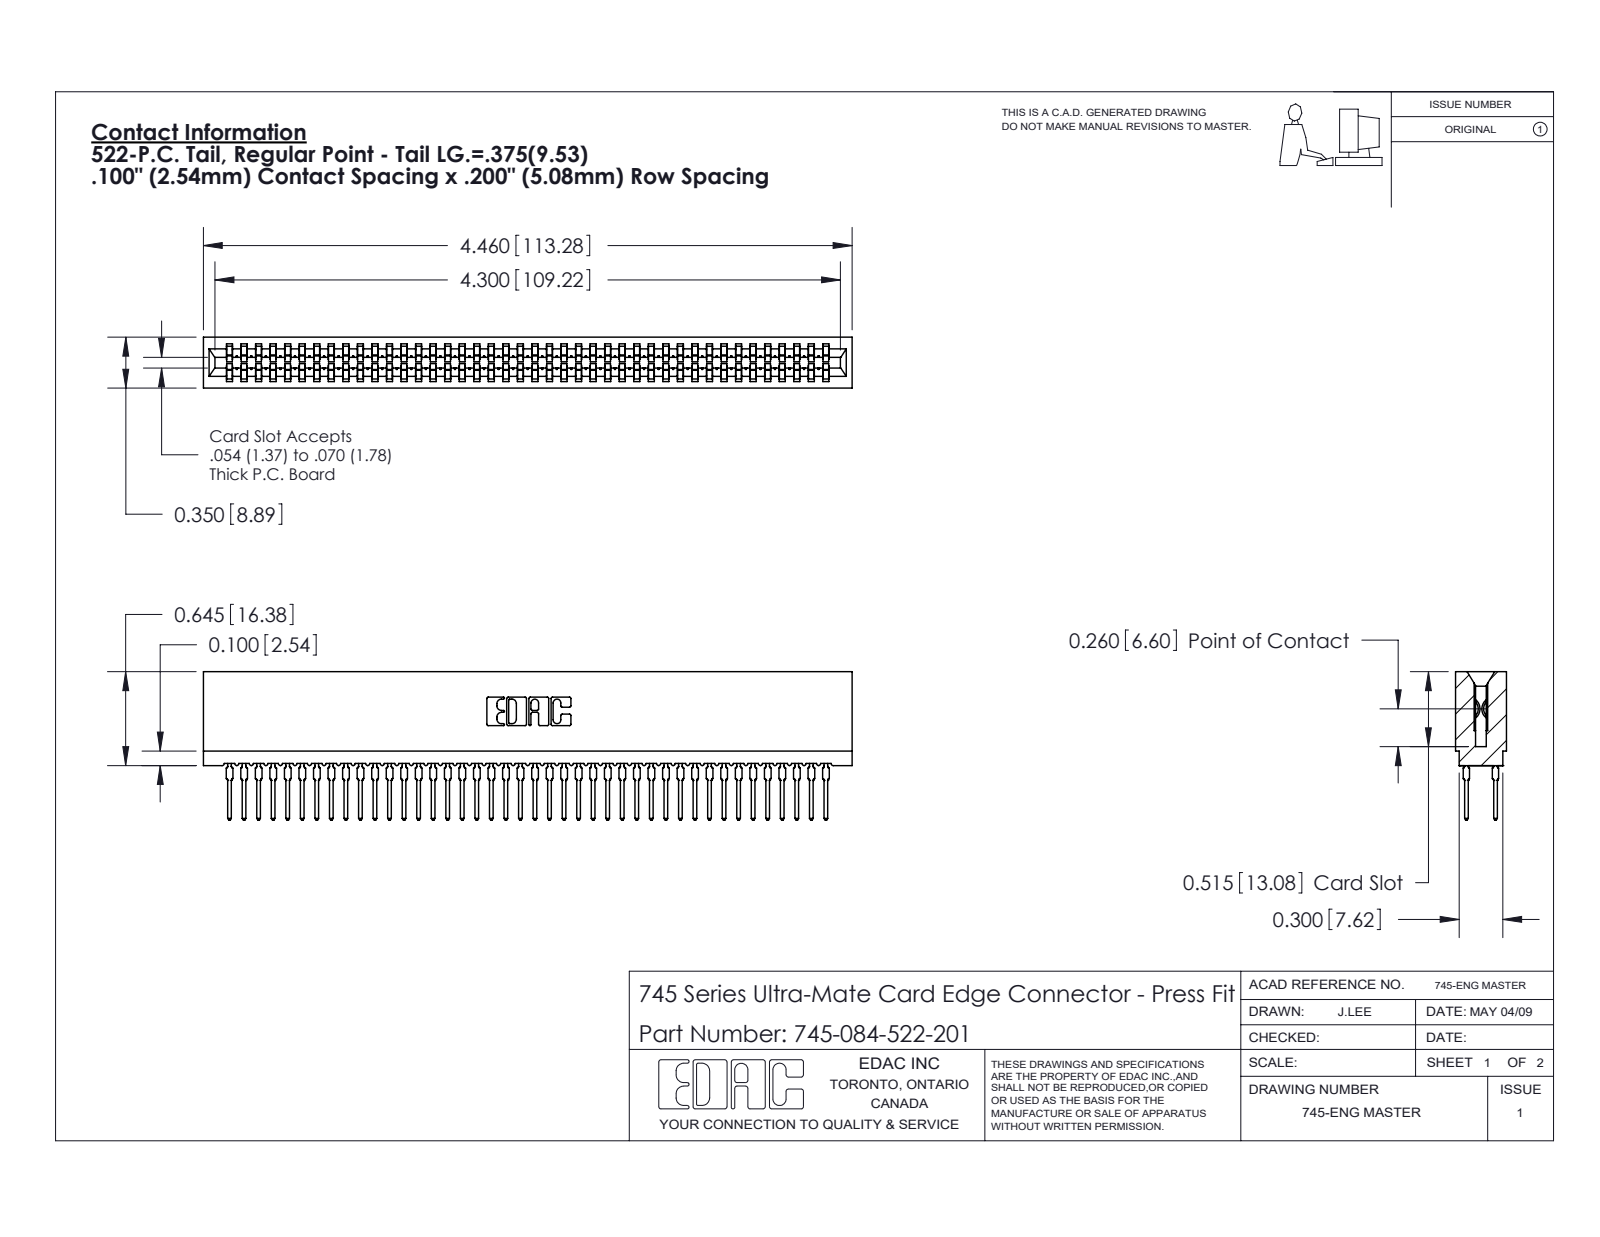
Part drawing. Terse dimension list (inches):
name: 745-292-001_522; 745-084-522-201; 745 Part_Insulator Option - 01
written by: SolidWorks 2020 (CONFIG_CONTROL_DESIGN)
unit: in
bodies: 85 solids, 7613 faces (3919 planar, 1510 cylindrical, 2184 other)
size: 4.46 × 1.021 × 0.35
volume: 0.628 in³; area: 32.88 in²
rounds: 168× R0.021, 84× R0.015, 22× R0.01, 8× R0.005, 8× R0.011, 6× R0.007, 6× R0.031, 3× R0.026
face distances: 0.35, 0.2, 0.063, 0.287, 0.138, 0.212, 0.076, 0.149, 0.045, 0.305
